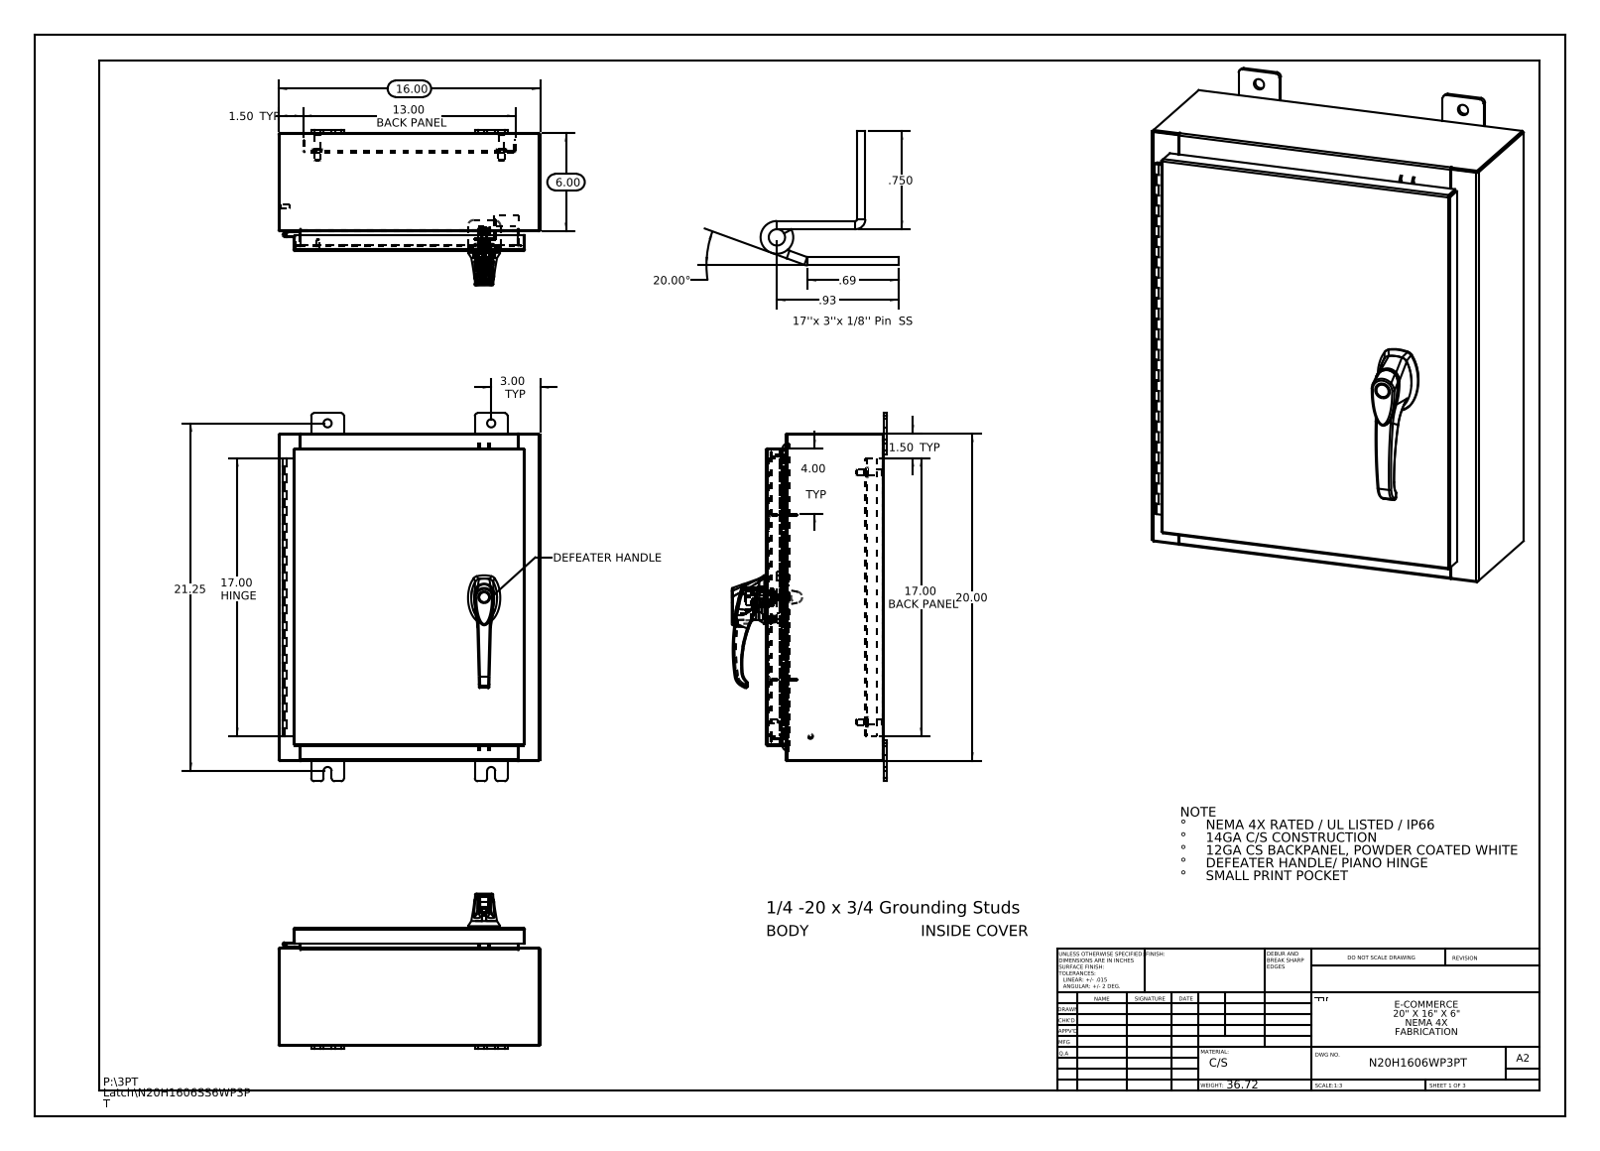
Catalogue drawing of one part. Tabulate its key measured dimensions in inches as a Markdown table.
| quantity | value |
| --- | --- |
| part name | N20H1606SS6WP3PT; N20H1606SS6WP3PT Defeater Handle - 3 - 2500-51 ZN; 26161102; N20H1606SS6WP3PT 263033_Industrilas (+8 more) |
| STEP written by | SolidWorks 2013 (CONFIG_CONTROL_DESIGN) |
| units | inches |
| bodies | 31 solids, 2316 faces (817 planar, 845 cylindrical, 654 other) |
| overall size | 22.5 × 16 × 9.495 |
| volume | 131.8 in³ |
| surface area | 3 230 in² |
| round holes (diameter × count) | 0.5 × 8, 0.25 × 4, 0.138 × 3, 0.161 × 3, 0.079 × 2, 0.203 × 2, 0.313 × 2, 0.437 × 2, 0.125 × 1, 0.125 × 1, 0.197 × 1, 0.276 × 1 |
| round bosses / shafts (diameter × count) | 0.625 × 4, 0.375 × 4, 0.33 × 4, 1.181 × 1, 0.748 × 1, 0.68 × 1, 0.661 × 1, 0.639 × 1 |
| partial cylindrical surfaces (radius × count) | 0.118 × 37, 0.006 × 33, 0.19 × 24, 0.013 × 22, 0.088 × 18, 0.039 × 15, 0.028 × 12, 0.008 × 6 |
| main face-to-face distances | 0.075, 7.126, 7.051, 7.201, 0.104, 15.925, 1, 1.075, 6.051, 6.126 |
| hole center spacings | 3.404, 11.975, 0.295, 0.625, 0.841, 1.25, 1.313, 1.561 |
